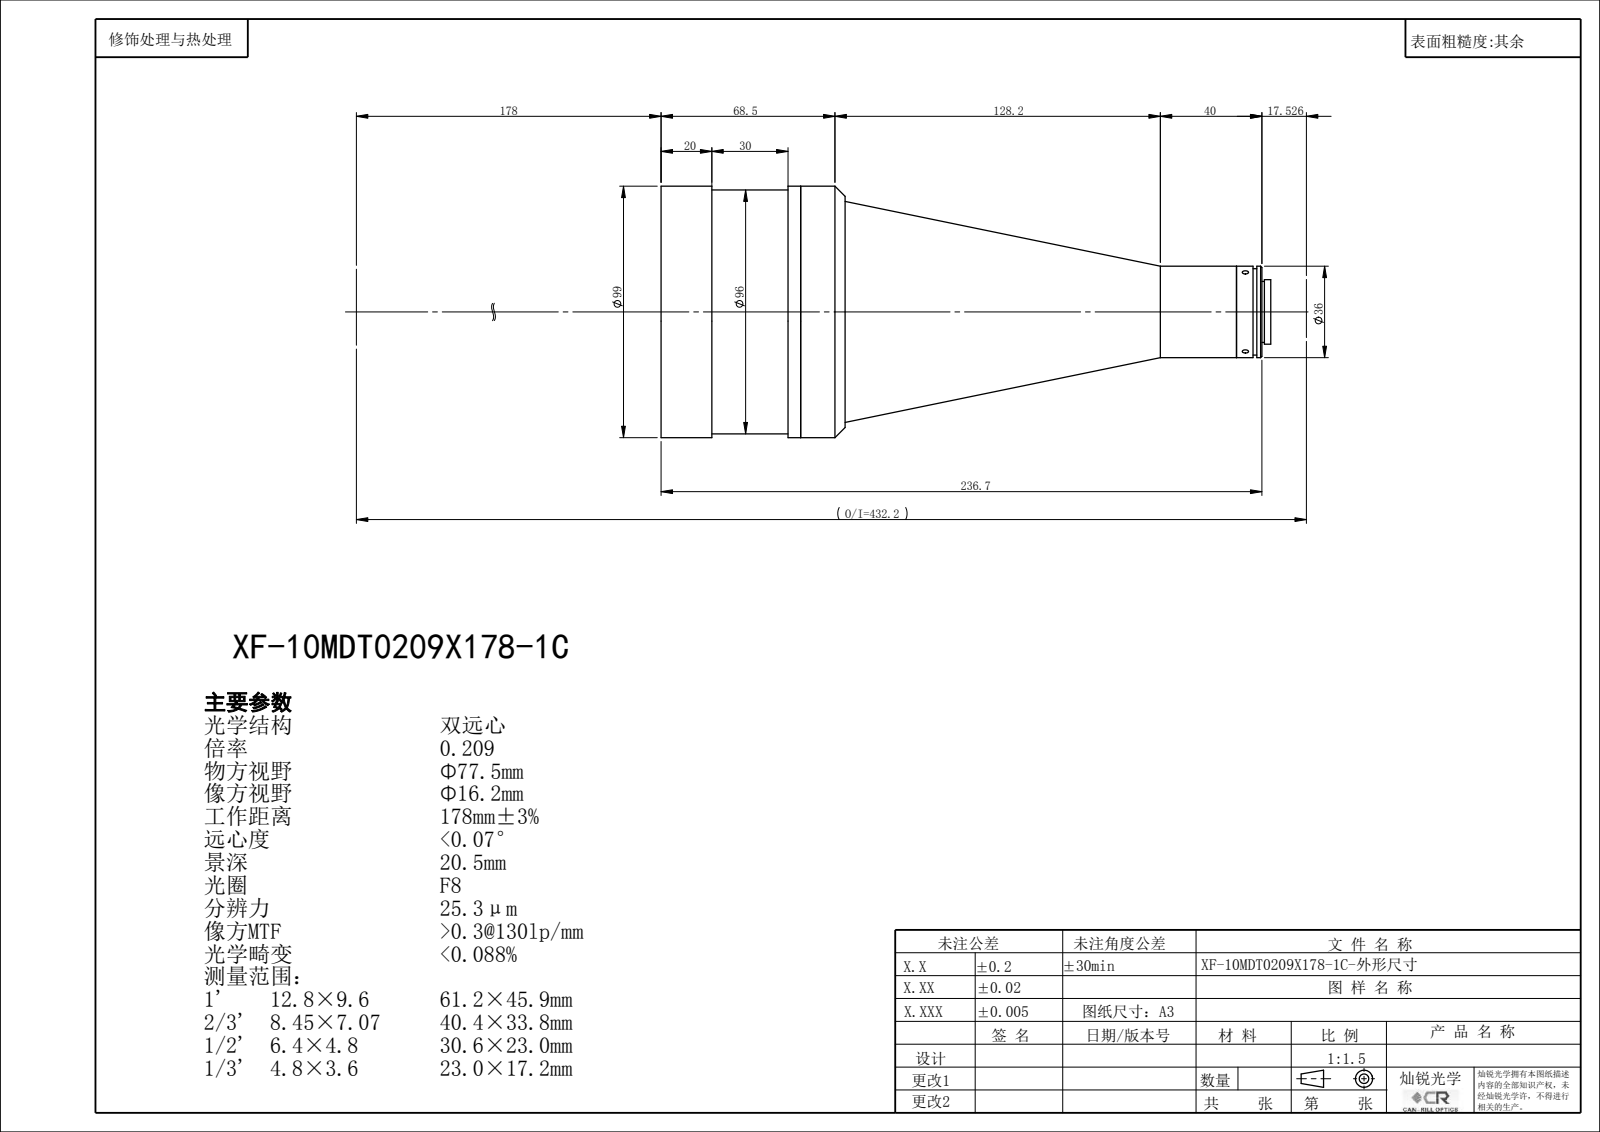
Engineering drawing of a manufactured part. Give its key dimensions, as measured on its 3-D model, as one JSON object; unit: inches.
{"step_written_by": "SolidWorks 2014 (CONFIG_CONTROL_DESIGN)", "units": "inches", "bodies": {"solids": 0, "faces": 86, "planar": 30, "cylindrical": 42, "other": 14}, "overall_size": [9.456, 3.898, 3.898], "round_holes": [[0.098, 3], [0.843, 1], [0.866, 1], [0.961, 1], [1.024, 1], [3.346, 1], [3.425, 1], [3.622, 1]], "round_bosses_or_shafts": [[3.898, 1], [3.78, 1], [1.417, 1], [1.339, 1], [1, 1], [0.945, 1]], "face_to_face_distances": [2.165, 0.375, 1.79, 2.854, 2.479, 0.689, 9.318, 8.943, 7.152, 6.463]}
